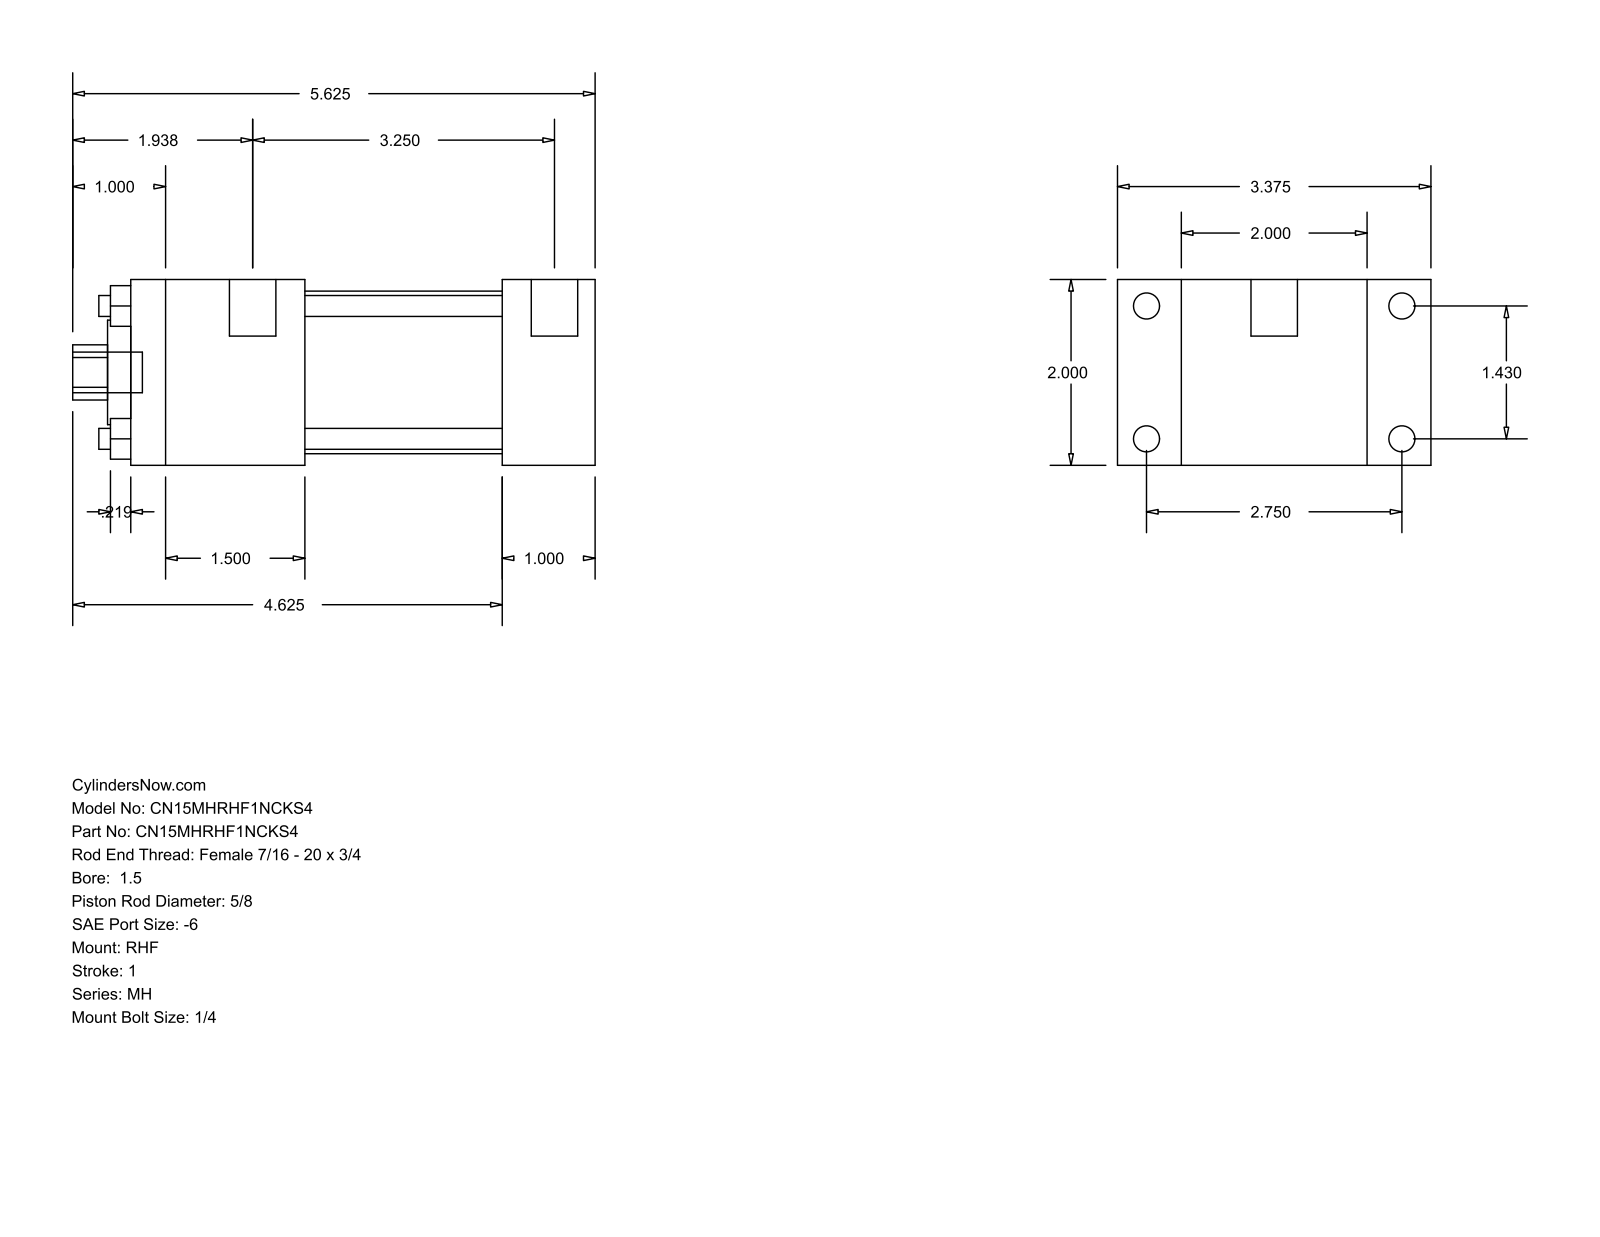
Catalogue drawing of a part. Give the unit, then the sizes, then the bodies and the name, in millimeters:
Units: millimetres
Overall size (bounding box): 142.88 × 85.72 × 50.8
Round holes (diameter × count): ⌀5.71 ×4, ⌀15.88 ×1, ⌀28.57 ×1, ⌀44.45 ×1
Round bosses / shafts (diameter × count): ⌀7.14 ×4, ⌀5.56 ×4, ⌀12.7 ×2, ⌀11.11 ×1
Partial cylindrical surfaces — rounded edges, fillets, slot ends (radius × count): R7.54 ×1
Main face-to-face distances: 50.8, 17.46, 68.26, 25.41, 101.59, 127, 53.97, 85.72, 47.62, 79.38
Hole centre spacings: 25.68, 36.32, 51.36
Bodies: 0 solids, 88 faces (60 planar, 28 cylindrical, 0 other)
Part name (STEP PRODUCT): MH_RHF__0150_0.625
STEP written by: GSSL Pune (CONFIG_CONTROL_DESIGN)
